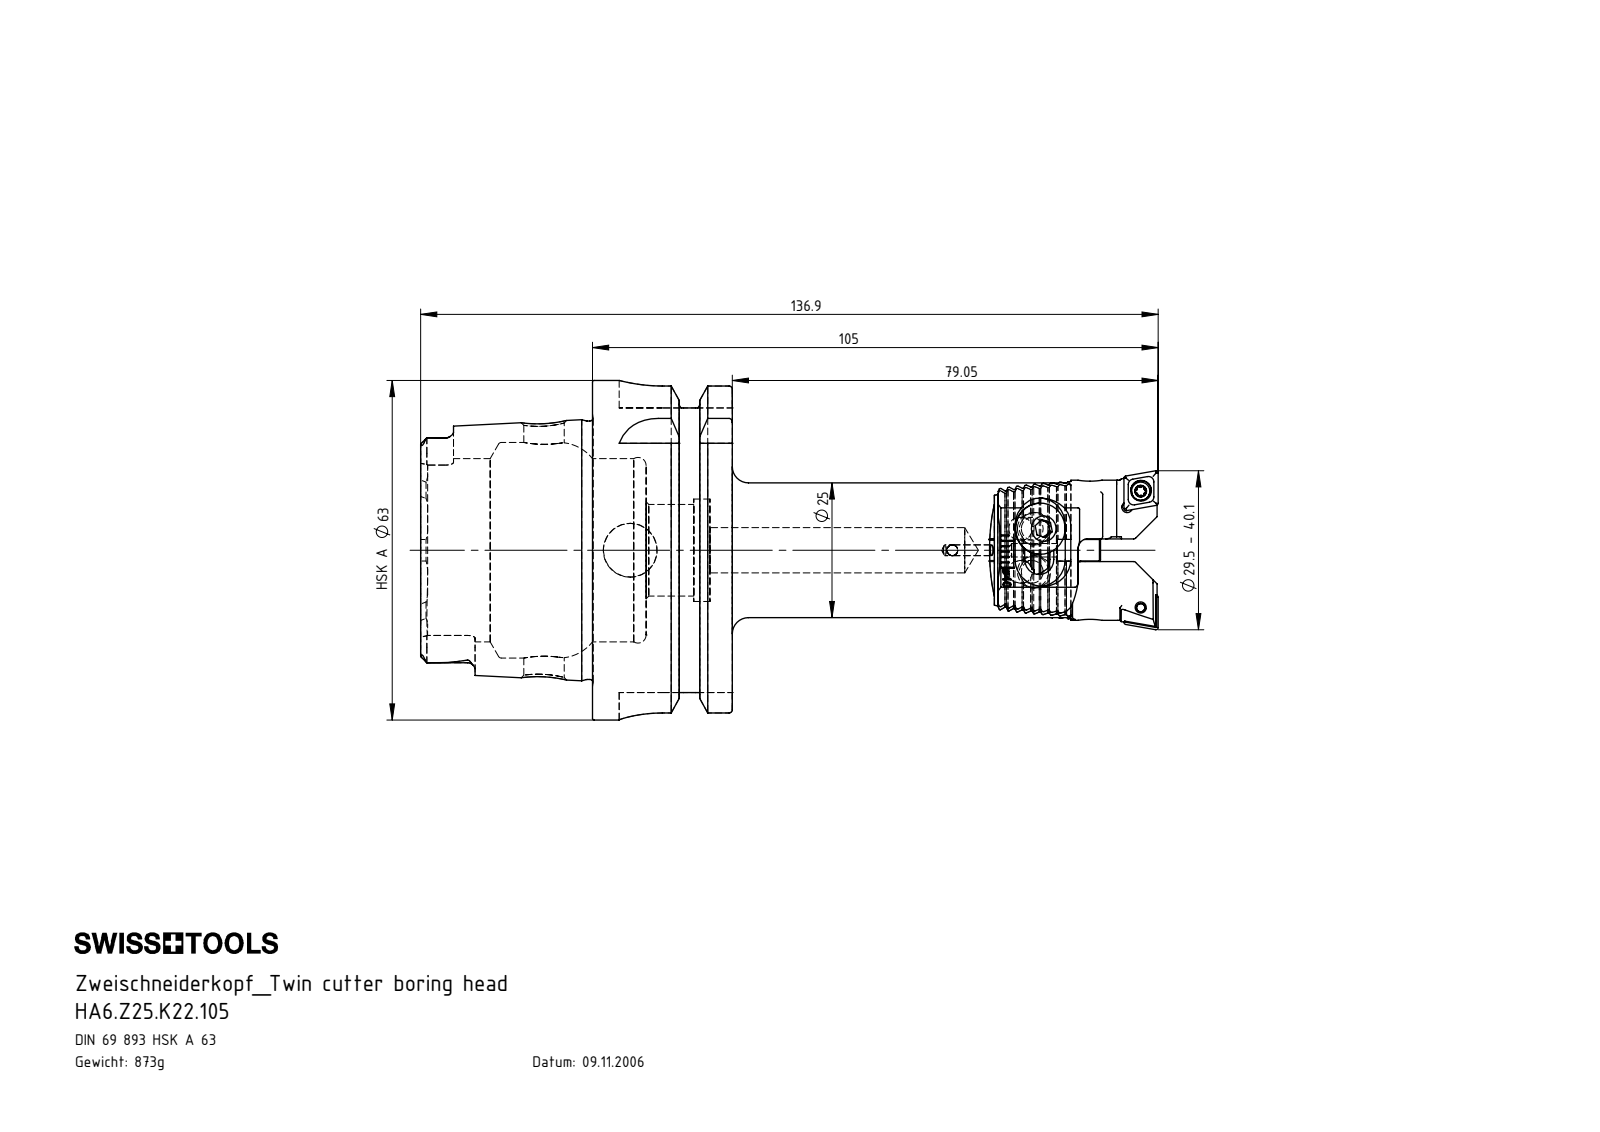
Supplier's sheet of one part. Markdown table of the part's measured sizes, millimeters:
| quantity | value |
| --- | --- |
| part name | Z25-WCA.001.016; Z25-ER1.002.012_A; HA6.Z25.K22.105; Z25-ER1.001.012 (+7 more) |
| STEP written by | SolidWorks 2022 (CONFIG_CONTROL_DESIGN) |
| units | millimeters |
| bodies | 14 solids, 1086 faces (502 planar, 279 cylindrical, 305 other) |
| overall size | 136.9 × 63 × 63 |
| volume | 111 630 mm³ |
| surface area | 34 644 mm² |
| round holes (diameter × count) | 2 × 5, 1.6 × 2, 2.05 × 2, 2.8 × 2, 3.85 × 2, 4.2 × 2, 5.3 × 2, 6 × 2, 2.5 × 1, 3.5 × 1, 7.5 × 1, 8.4 × 1 |
| round bosses / shafts (diameter × count) | 9.5 × 2, 9.2 × 2, 5 × 2, 3.4 × 2, 2.5 × 2, 63 × 1, 54.95 × 1, 47.94 × 1 |
| partial cylindrical surfaces (radius × count) | 0.12 × 18, 0.5 × 18, 0.12 × 16, 0.21 × 12, 0.36 × 10, 1.4 × 6, 2 × 4, 2.8 × 4 |
| main face-to-face distances | 25.95, 1.43, 16, 9.95, 2.86, 1.39, 5.71, 52.8, 31.9, 41.85 |
| hole center spacings | 3.9, 4, 7, 18.02, 18.11, 20.91, 103.38, 13.52 |
